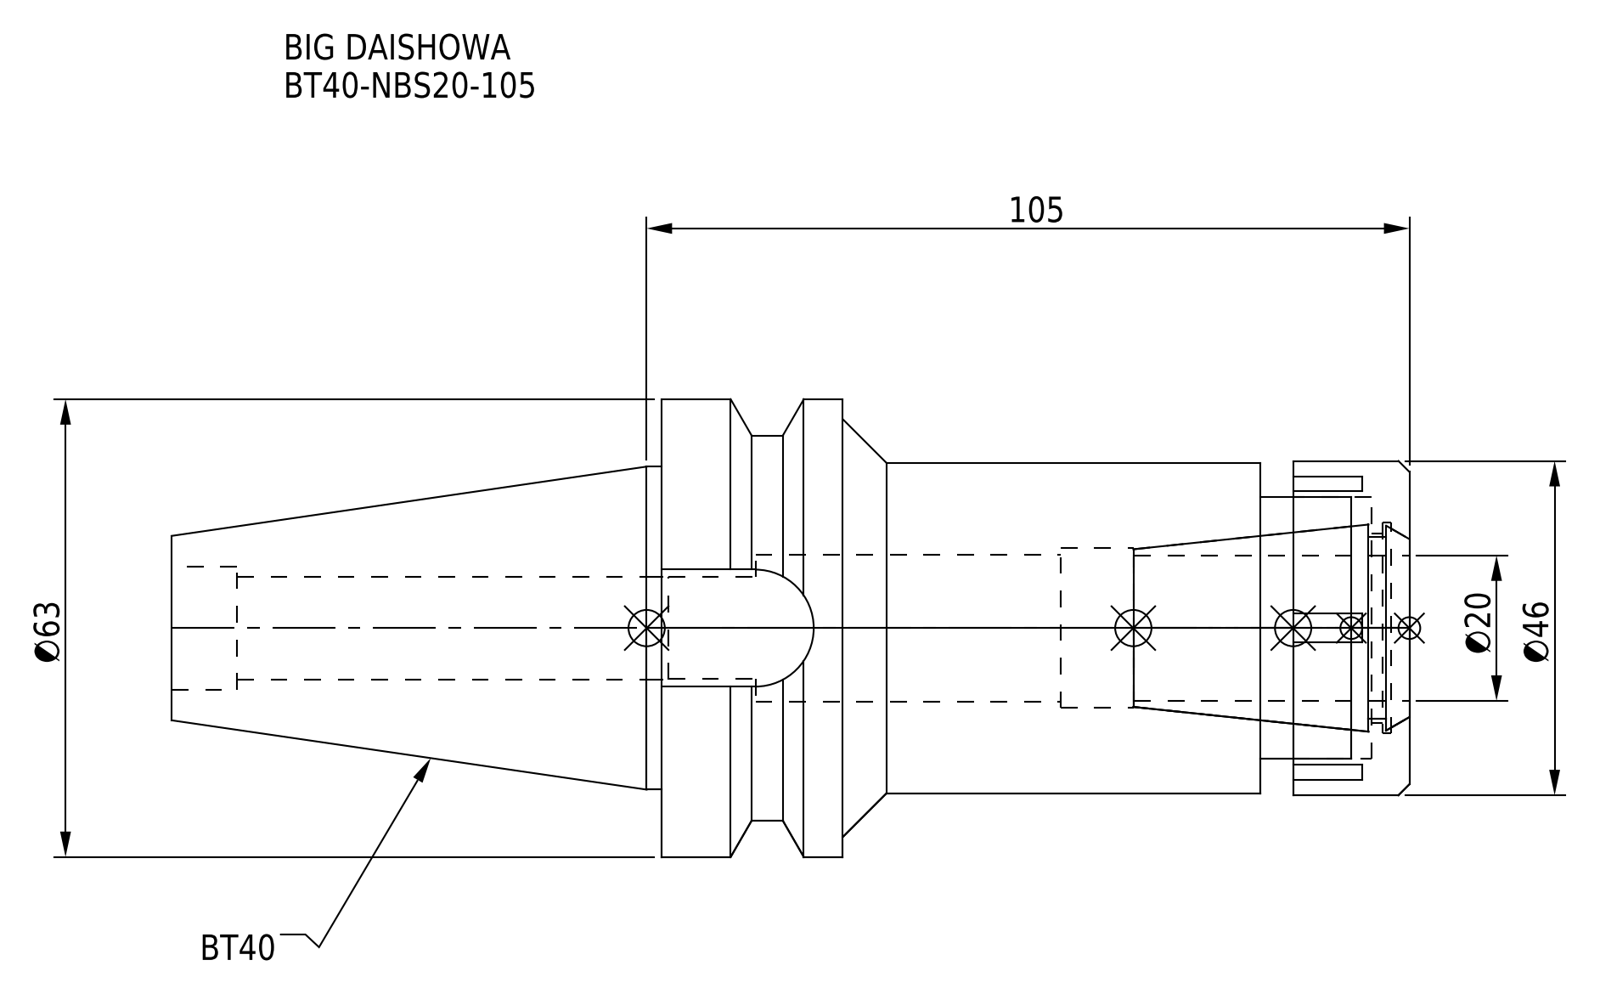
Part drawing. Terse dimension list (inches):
name: BT40-NBS20-105_1.stp; BT40-NBS20-105.stp; BT40-NBS20-105-FreeParts; BT40-NBS20-105 (+3 more)
written by: SolidWorks 2019 (CONFIG_CONTROL_DESIGN)
unit: in
bodies: 2 solids, 93 faces (45 planar, 34 cylindrical, 14 other)
size: 6.709 × 2.48 × 2.48
volume: 12.81 in³; area: 67.38 in²
holes: 1× ⌀0.551, 1× ⌀0.559, 1× ⌀0.669, 1× ⌀0.799, 1× ⌀0.866, 1× ⌀1.024, 1× ⌀1.142, 1× ⌀1.417
bosses: 1× ⌀2.48, 1× ⌀2.087, 1× ⌀1.811, 1× ⌀1.791, 1× ⌀1.75
rounds: 1× R0.317
face distances: 4.055, 0.315, 0.807, 3.248, 0.63, 0.177, 3.425, 3.071, 2.441, 2.264
